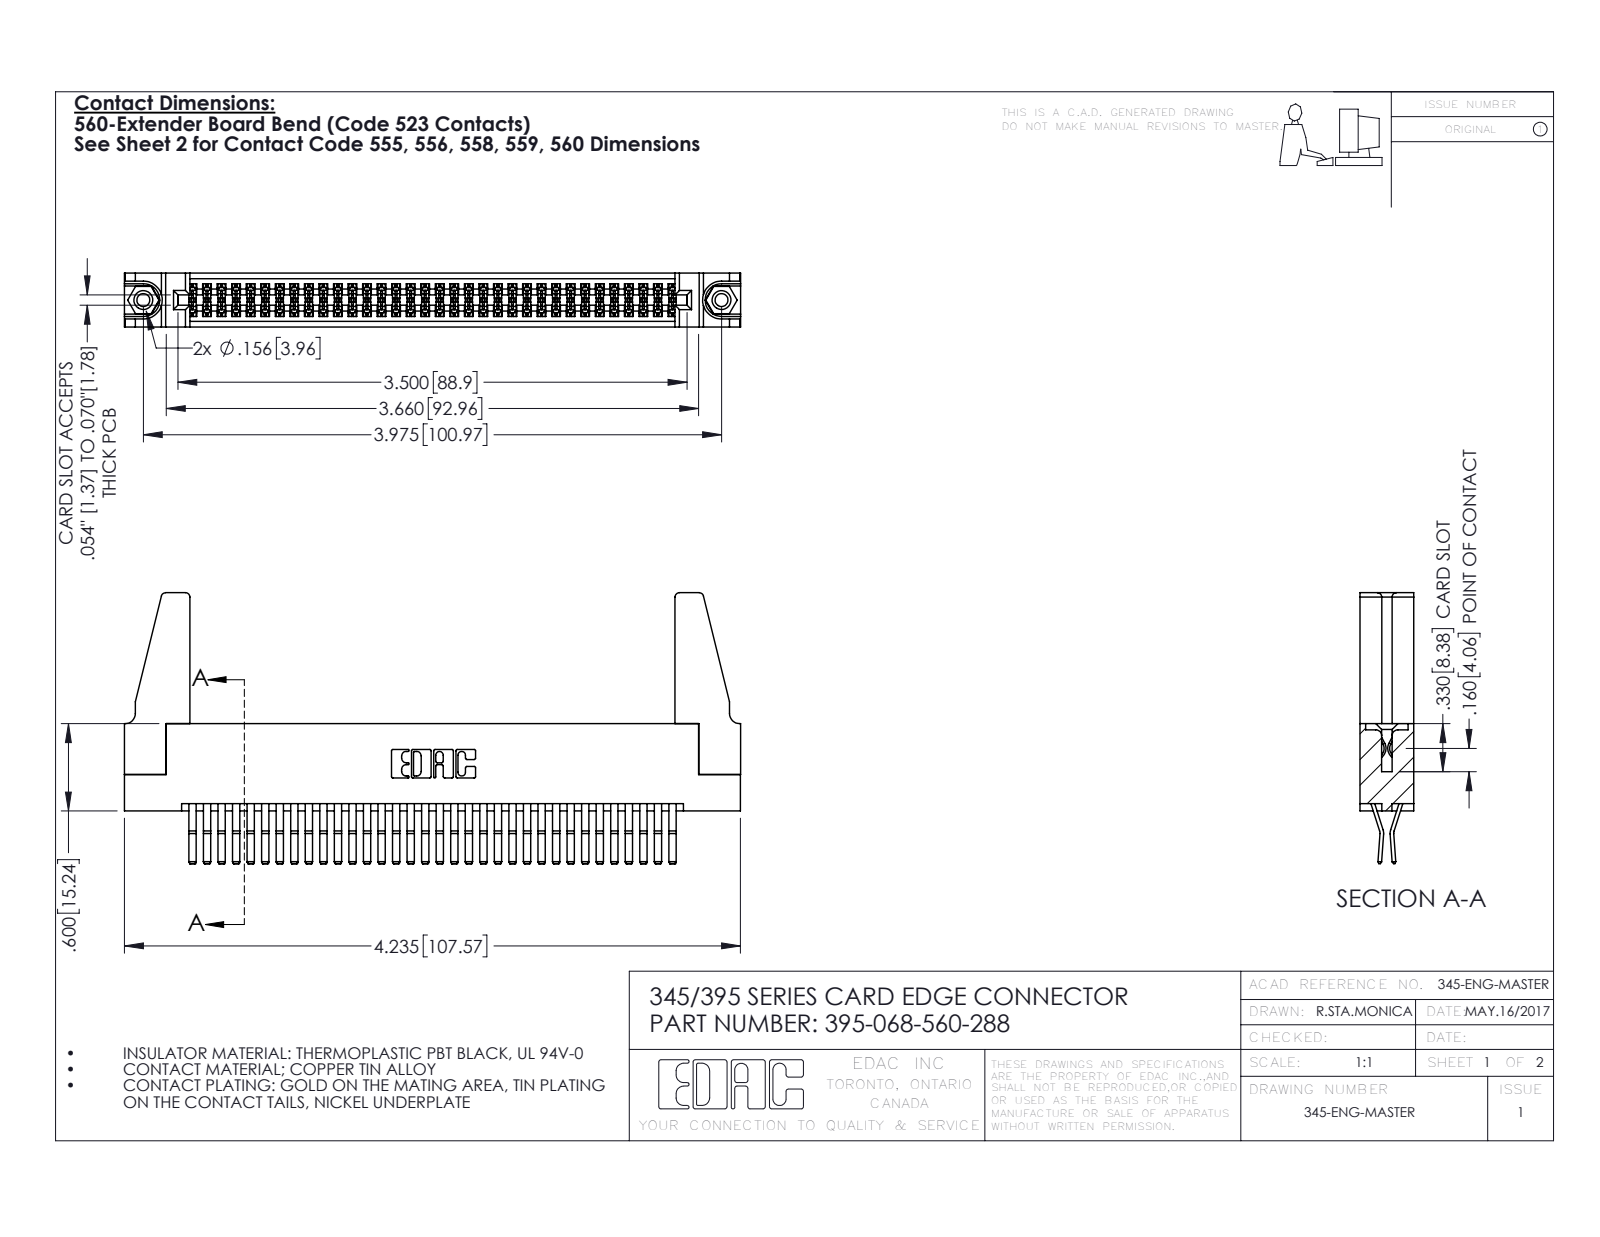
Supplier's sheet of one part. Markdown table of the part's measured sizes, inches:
| quantity | value |
| --- | --- |
| part name | 345 Part_Flush Mounting Lugs - 0.156 Dia-TH; 345-220-078_345-220-088; 345-292-001_560 Tail; 395-068-560-288 (+1 more) |
| STEP written by | SolidWorks 2016 (CONFIG_CONTROL_DESIGN) |
| units | inches |
| bodies | 73 solids, 3786 faces (2396 planar, 1374 cylindrical, 16 other) |
| overall size | 4.236 × 1.862 × 0.37 |
| volume | 0.859 in³ |
| surface area | 31.17 in² |
| round holes (diameter × count) | 0.089 × 2, 0.125 × 2, 0.156 × 2, 0.064 × 1 |
| round bosses / shafts (diameter × count) | 0.155 × 2 |
| partial cylindrical surfaces (radius × count) | 0.006 × 102, 0.01 × 22, 0.03 × 8, 0.007 × 6, 0.031 × 6, 0.026 × 3, 0.01 × 2, 0.014 × 2 |
| main face-to-face distances | 0.072, 0.298, 0.025, 0.37, 0.2, 0.098, 0.272, 0.225, 0.175, 0.149 |
| hole center spacings | 0.27, 3.74, 3.975 |
